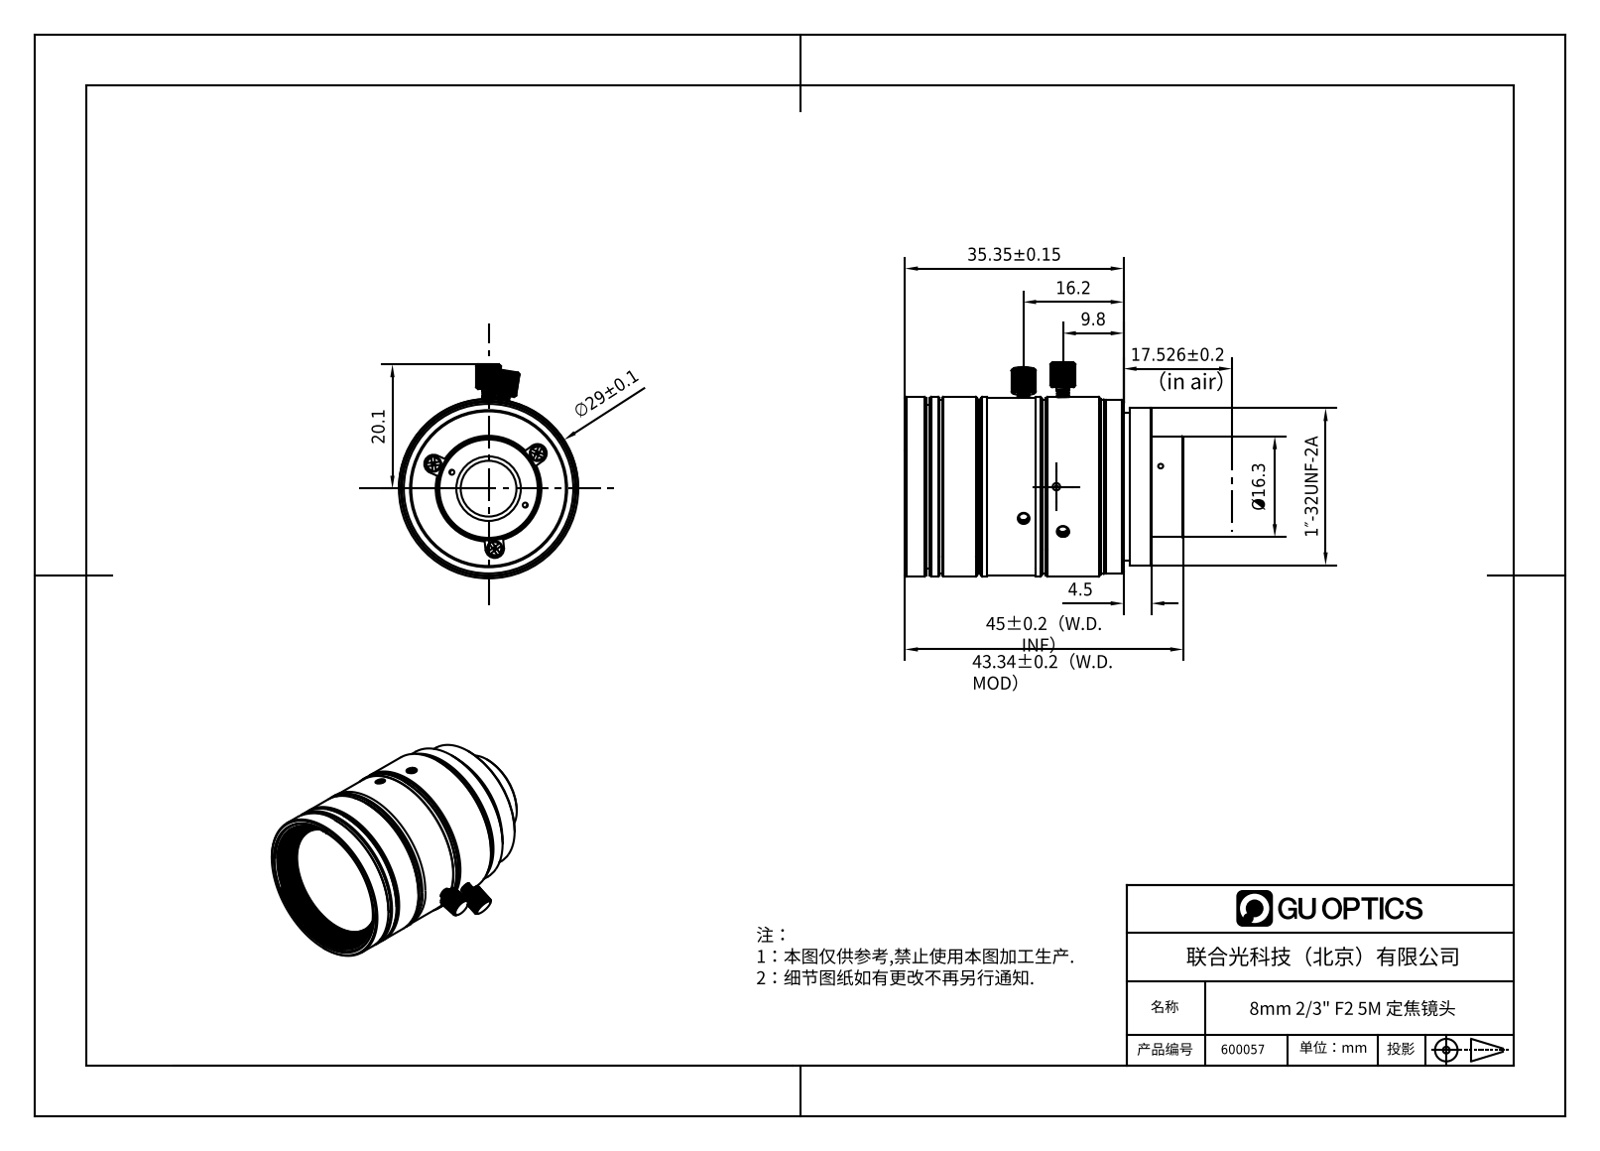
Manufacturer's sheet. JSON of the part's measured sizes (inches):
{"part_name": "600057", "step_written_by": "SolidWorks 2020 (CONFIG_CONTROL_DESIGN)", "units": "inches", "bodies": {"solids": 9, "faces": 1040, "planar": 281, "cylindrical": 545, "other": 214}, "overall_size": [1.771, 1.322, 1.142], "volume_in3": 1.522, "surface_area_in2": 16.92, "round_holes": [[0.063, 5], [0.079, 5], [0.031, 3], [0.067, 3], [0.114, 1], [0.355, 1], [0.391, 1], [0.531, 1], [0.657, 1], [0.861, 1], [0.872, 1], [0.874, 1]], "round_bosses_or_shafts": [[0.063, 6], [0.098, 3], [0.047, 3], [1.142, 2], [1.11, 2], [0.079, 2], [1.134, 1], [1.102, 1]], "partial_cylinders_radius": [[0.044, 6], [0.133, 6], [0.135, 6], [0.024, 3], [0.059, 3], [0.006, 2], [0.044, 2], [0.079, 2]], "face_to_face_distances": [0.157, 0.118, 0.059, 0.217, 0.079, 0.38, 1.285, 0.039, 0.177, 1.352], "hole_center_spacings": [0.383, 0.256, 0.384, 0.665, 0.128, 0.256, 0.256, 0.338]}
